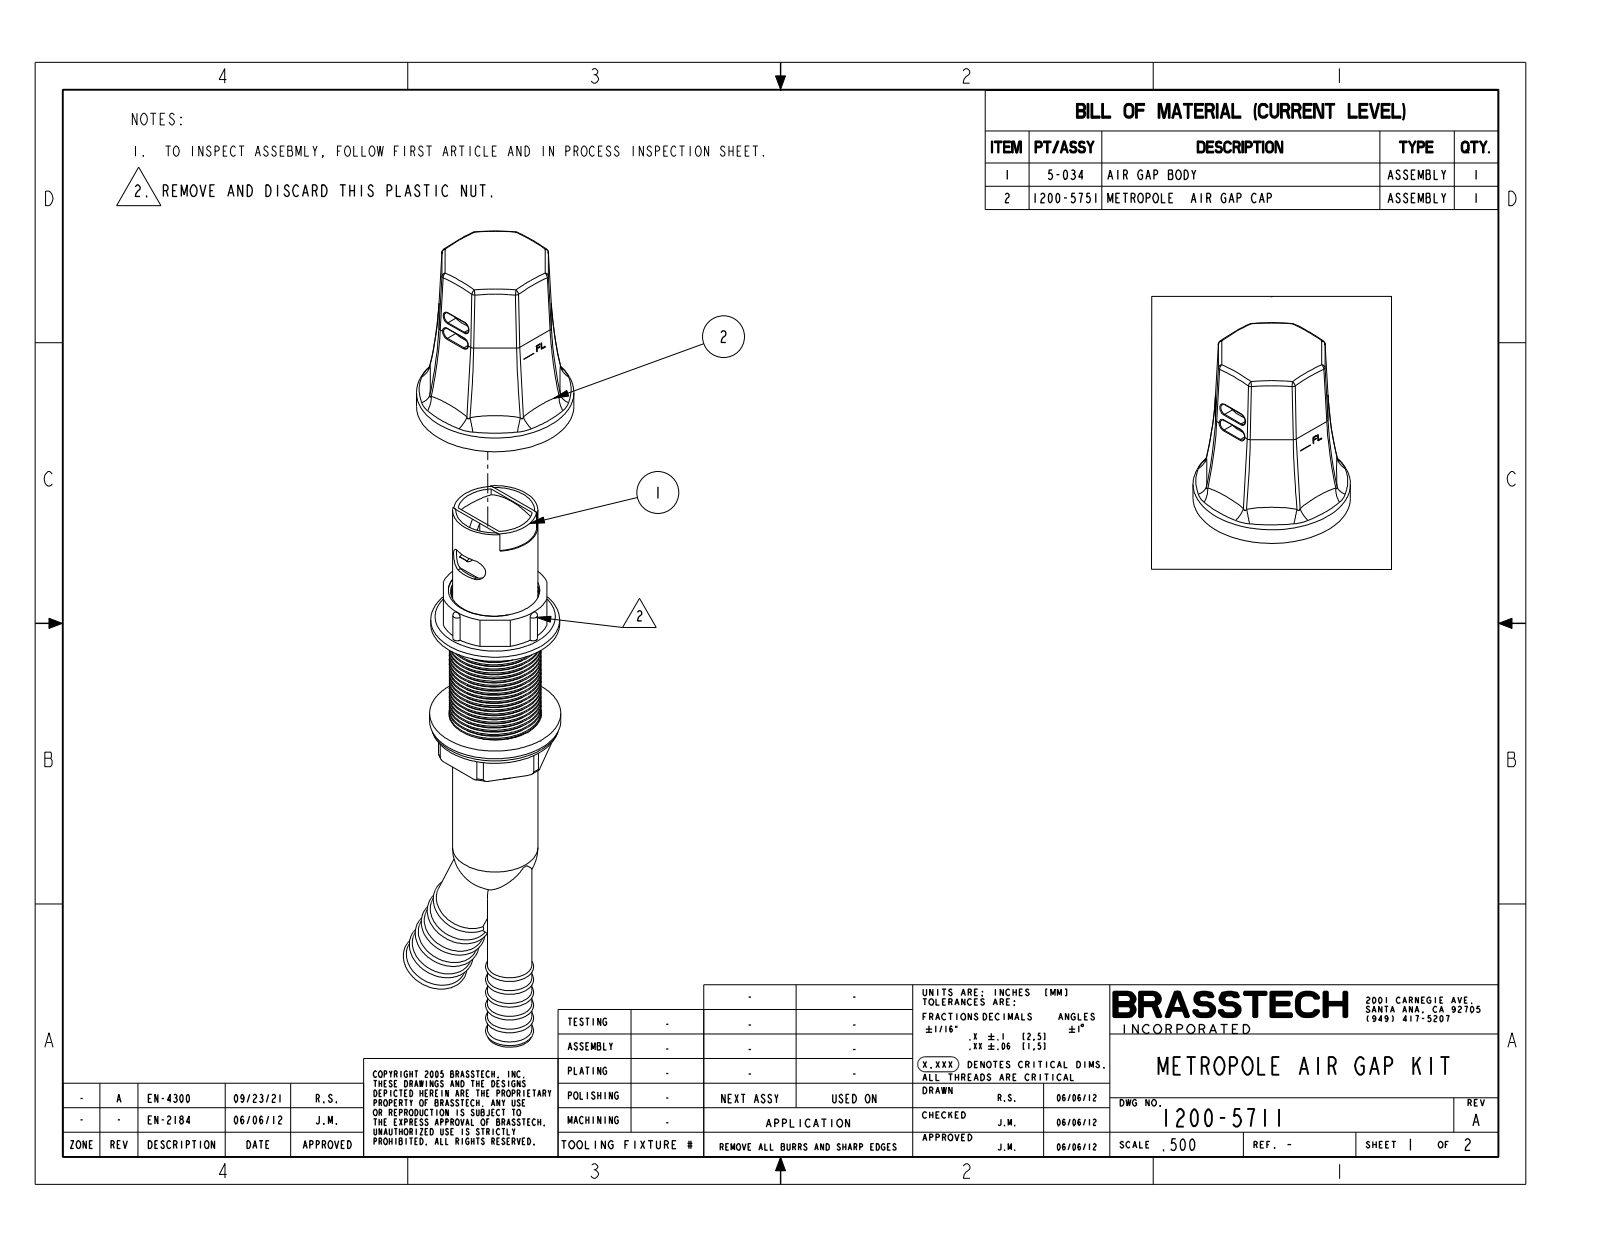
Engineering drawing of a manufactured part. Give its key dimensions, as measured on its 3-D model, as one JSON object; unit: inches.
{"part_name": "1200-5711", "step_written_by": "CREO PARAMETRIC BY PTC INC, 2018400 (AUTOMOTIVE_DESIGN)", "units": "inches", "bodies": {"solids": 1, "faces": 341, "planar": 71, "cylindrical": 141, "other": 129}, "overall_size": [9.317, 2.662, 2.16], "volume_in3": 11.92, "surface_area_in2": 72.71, "round_holes": [[1.2, 1], [1.25, 1], [1.27, 1], [1.28, 1]], "round_bosses_or_shafts": [[2.16, 1], [1.8, 1], [1.76, 1], [1.259, 1], [1.17, 1], [0.854, 1], [0.61, 1]], "partial_cylinders_radius": [[0.06, 8], [0.04, 6], [0.079, 4], [0.01, 3], [0.157, 2]], "face_to_face_distances": [1.5, 3.9, 2.4, 3.14, 1.64, 0.76, 1.42, 0.345, 1.075, 0.61]}
